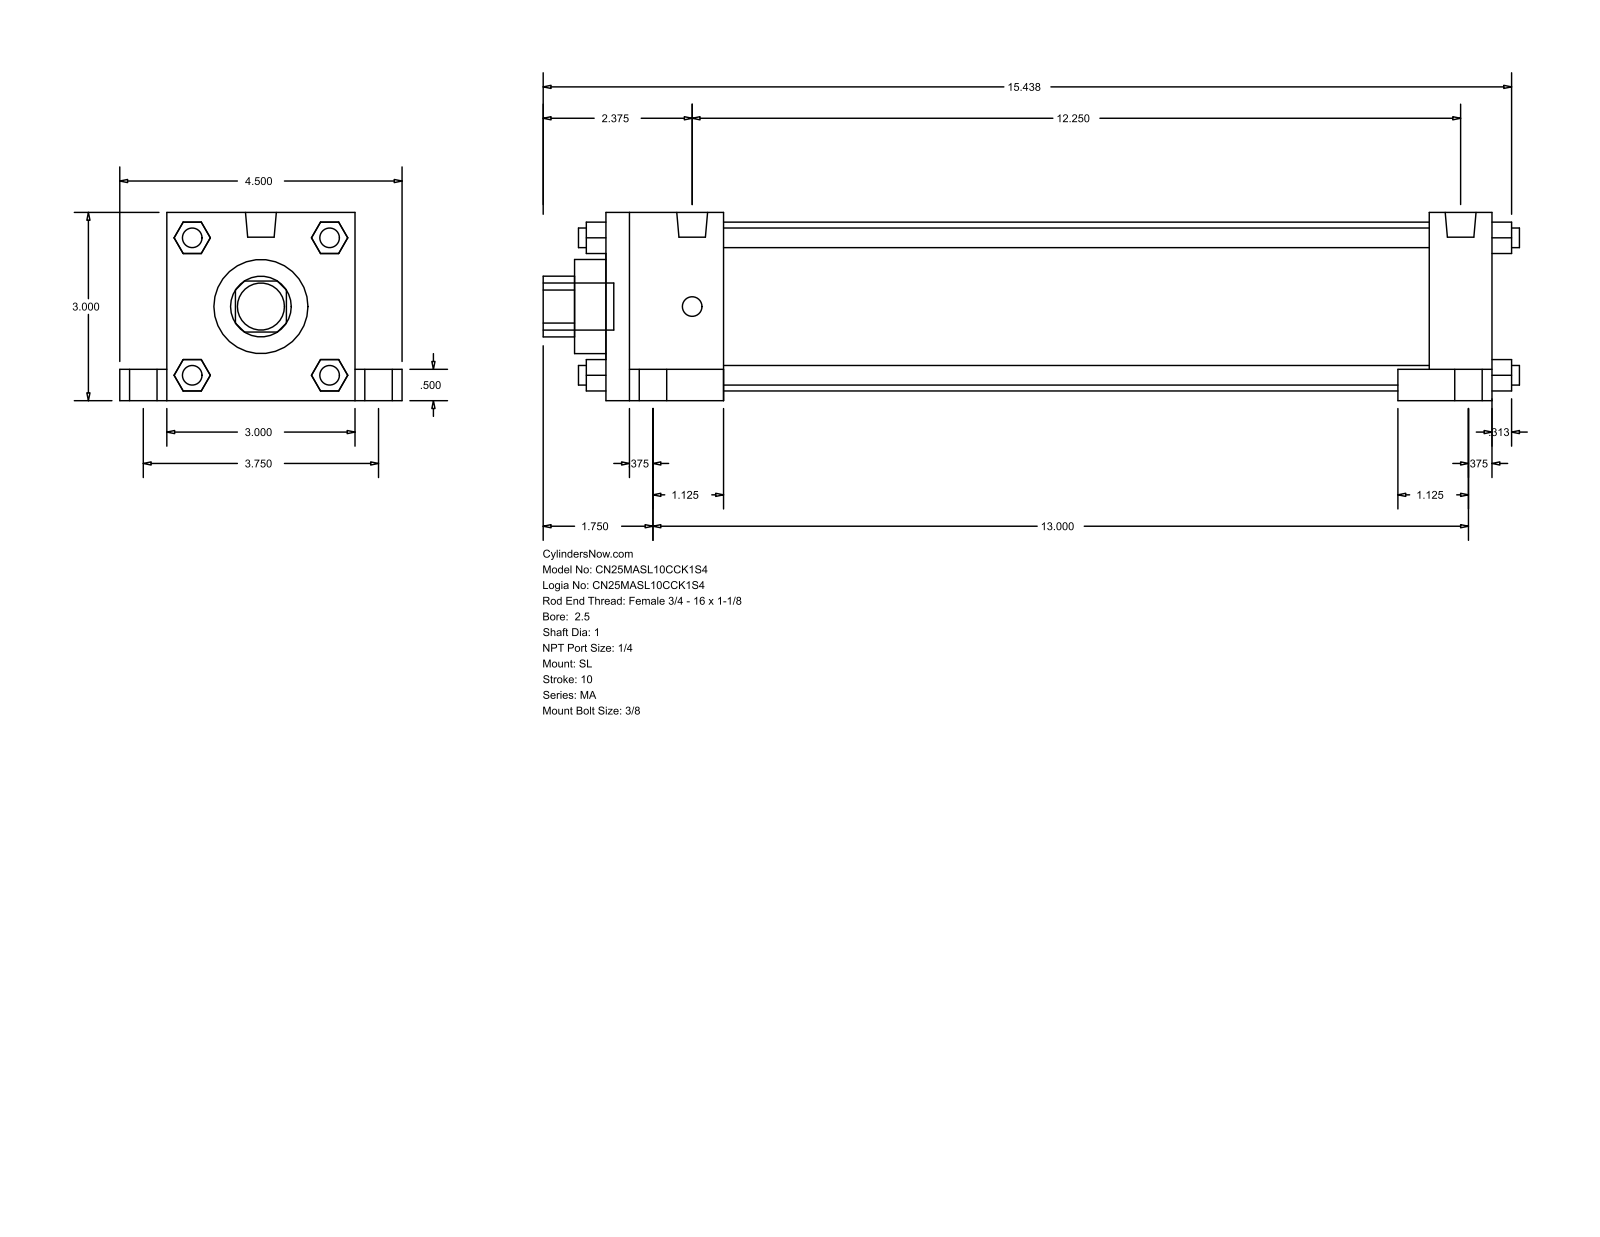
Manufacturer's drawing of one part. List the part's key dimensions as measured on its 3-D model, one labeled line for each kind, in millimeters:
Part name (STEP PRODUCT): MA_SL__0250_1
STEP written by: GSSL Pune (CONFIG_CONTROL_DESIGN)
Units: millimetres
Bodies: 0 solids, 148 faces (112 planar, 36 cylindrical, 0 other)
Overall size (bounding box): 395.29 × 114.3 × 76.2
Round holes (diameter × count): ⌀25.4 ×1, ⌀38.1 ×1, ⌀68.33 ×1
Round bosses / shafts (diameter × count): ⌀7.94 ×8, ⌀17.46 ×4, ⌀11.11 ×4, ⌀12.49 ×2, ⌀19.05 ×1
Partial cylindrical surfaces — rounded edges, fillets, slot ends (radius × count): R12.29 ×1
Main face-to-face distances: 76.2, 358.78, 12.7, 47.63, 311.15, 333.37, 285.74, 25.41, 19.05, 95.25
